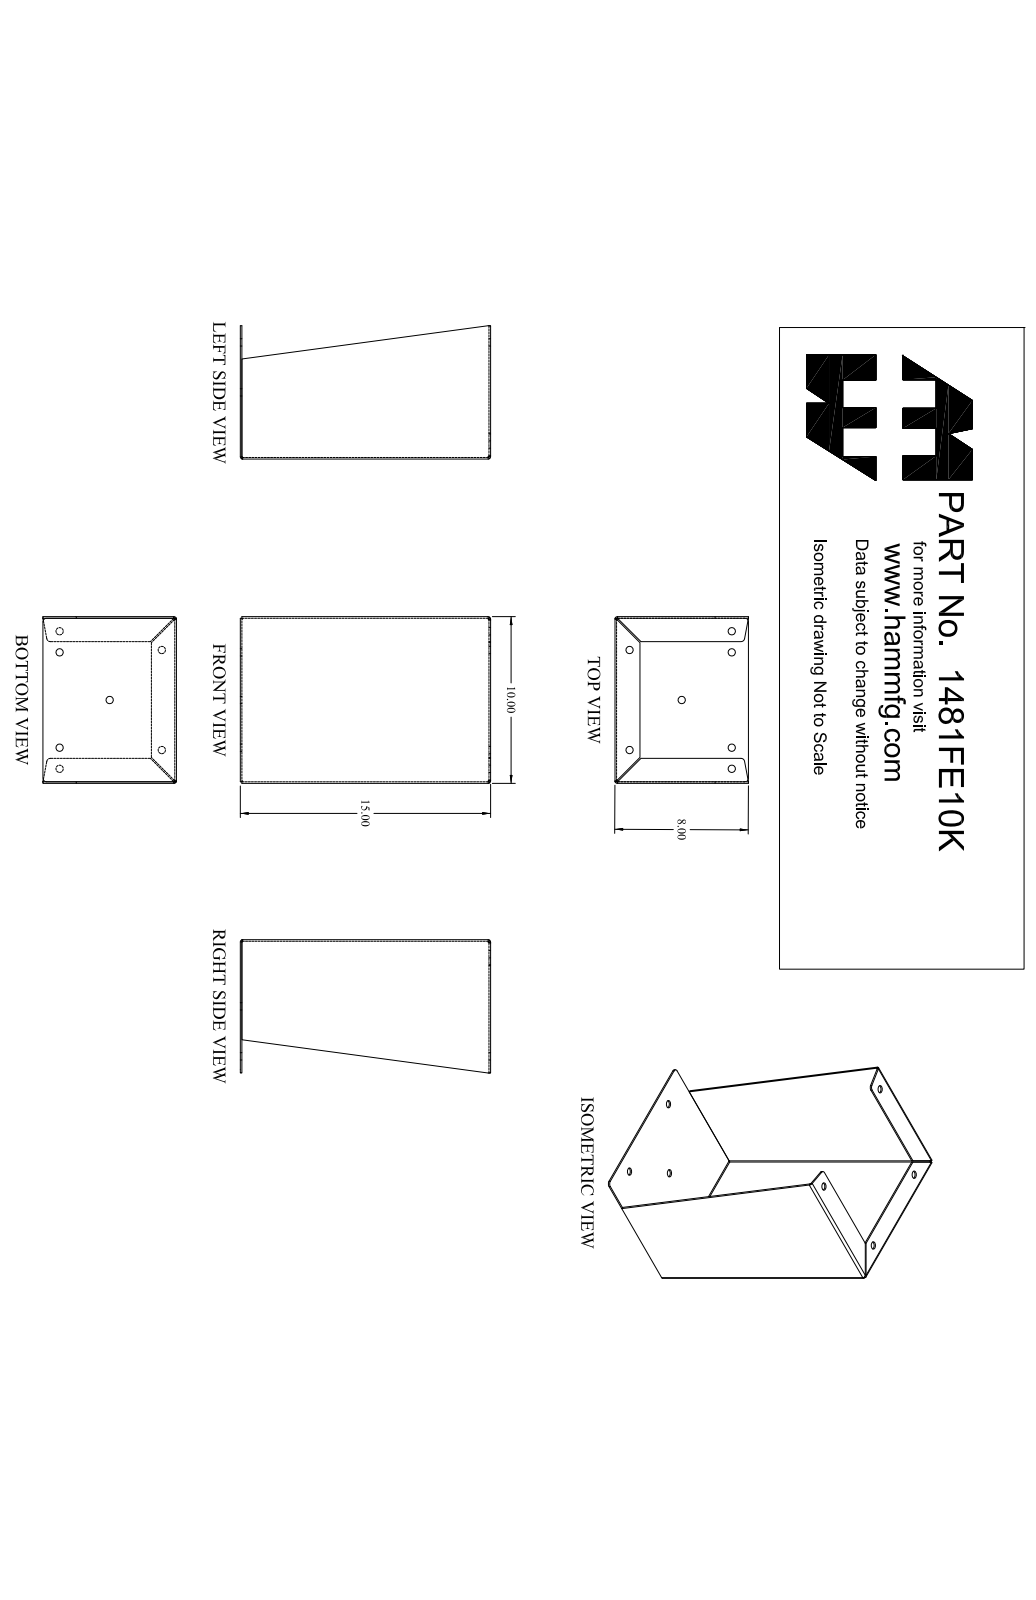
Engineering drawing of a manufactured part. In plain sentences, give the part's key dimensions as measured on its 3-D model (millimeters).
The part is named "1481FE10K_Default". Its 3-D file was written by "SolidWorks 2019 (CONFIG_CONTROL_DESIGN)". It is 1 solid with 78 faces: 42 planar, 30 cylindrical and 6 other. Overall it measures 381 by 254 by 203.2 millimeters. Its volume is 718 100 cubic millimeters and its surface area 601 700 square millimeters. Round holes: 7 of diameter 11.1. Partial cylindrical surfaces (rounded edges, fillets, slot ends): 6 of radius 1.2, 6 of radius 3.6, 4 of radius 5.6. The main face-to-face distances are 2.4, 251.6, 254, 249.2, 2.4, 376.2, 378.6, 378.6, 381, 35.7. The hole center spacings are 32.2, 105.3, 110, 129.6, 155.6, 158.2, 177.4, 215.3.
